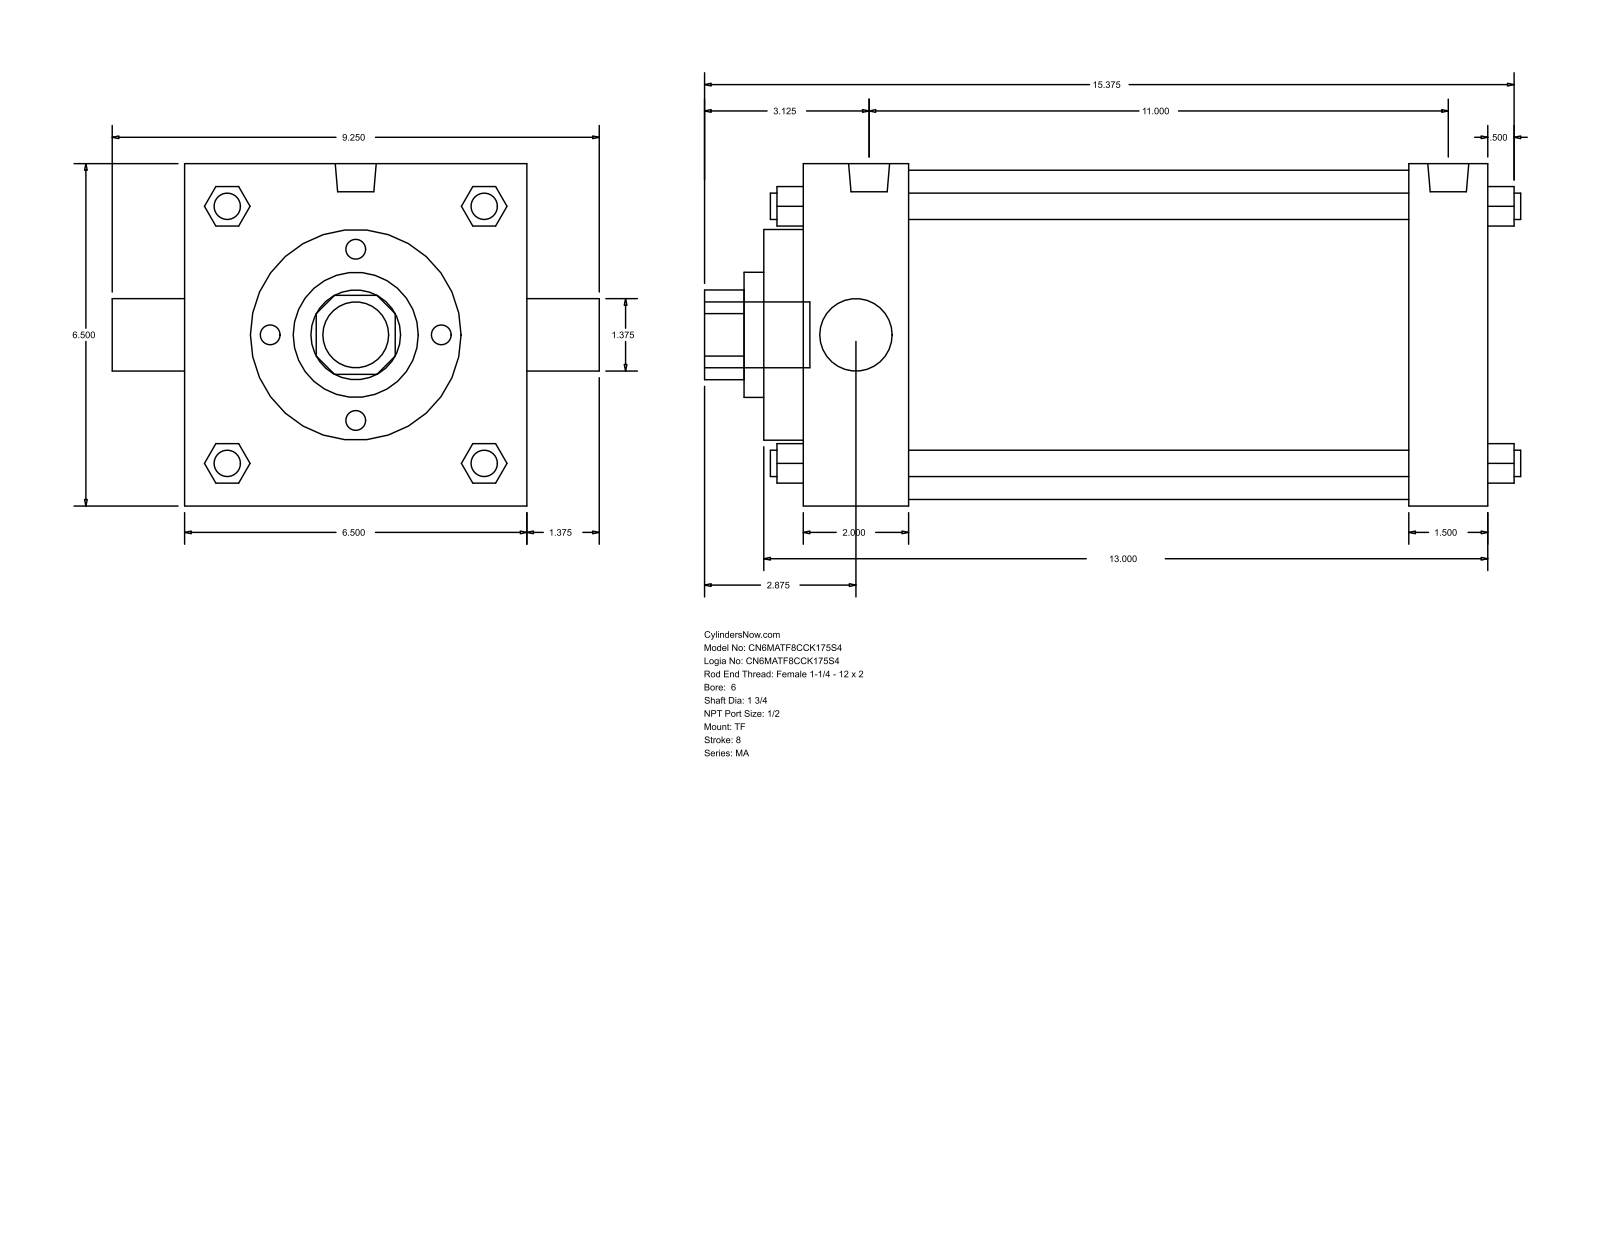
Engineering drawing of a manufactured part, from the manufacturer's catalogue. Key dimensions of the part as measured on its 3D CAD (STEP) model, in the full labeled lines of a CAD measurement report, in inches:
Part name (STEP PRODUCT): MA_TF__0600_1.75
STEP written by: GSSL Pune (CONFIG_CONTROL_DESIGN)
Units: inches
Bodies: 0 solids, 122 faces (93 planar, 29 cylindrical, 0 other)
Overall size (bounding box): 15.5 × 9.25 × 6.5
Round holes (diameter × count): ⌀1.375 ×1, ⌀1.75 ×1, ⌀2.375 ×1, ⌀4 ×1, ⌀6.25 ×1
Round bosses / shafts (diameter × count): ⌀0.5 ×4, ⌀0.687 ×3, ⌀0.778 ×2, ⌀1.25 ×1
Partial cylindrical surfaces — rounded edges, fillets, slot ends (radius × count): R0.852 ×1
Main face-to-face distances: 6.5, 13, 0.75, 2, 11, 11.5, 9.5, 1.5, 2.75, 12.25
